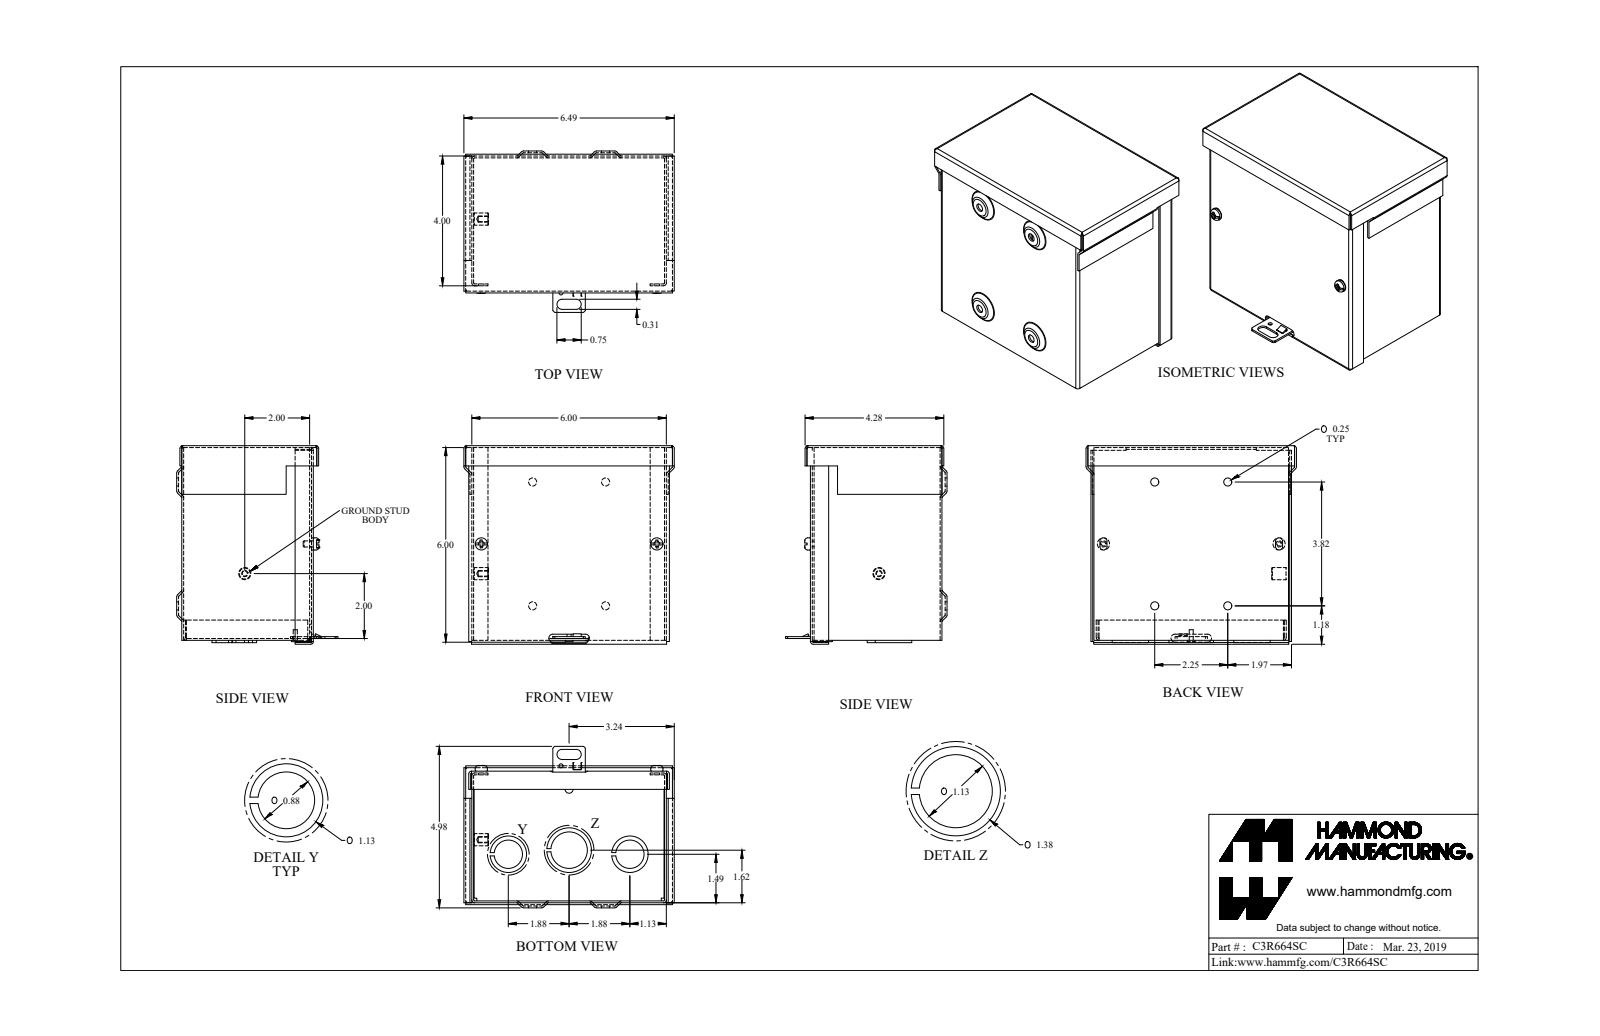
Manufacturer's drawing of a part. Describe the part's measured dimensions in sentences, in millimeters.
The part is named "C3R664SC_Default". Its 3-D file was written by "SolidWorks 2019 (CONFIG_CONTROL_DESIGN)". It is 9 solids with 353 faces: 182 planar, 97 cylindrical and 74 other. Overall it measures 164.8 by 155.4 by 126.4 millimeters. Its volume is 201 900 cubic millimeters and its surface area 282 600 square millimeters. Round holes: 4 of diameter 6.4, 2 of diameter 4.3, 2 of diameter 22.2, 1 of diameter 3.2, 1 of diameter 3.5, 1 of diameter 4, 1 of diameter 28.6. Round bosses or shafts: 3 of diameter 9.5, 2 of diameter 28.6, 2 of diameter 4.8, 1 of diameter 34.9, 1 of diameter 3.2. Partial cylindrical surfaces (rounded edges, fillets, slot ends): 21 of radius 0.7, 21 of radius 2.2, 8 of radius 3.2, 4 of radius 2.8, 2 of radius 4. The main face-to-face distances are 1.4, 101.6, 151, 152.4, 100.2, 1.4, 103, 149.5, 149.5, 151. The hole center spacings are 63, 108.7, 57.2, 97, 112.5, 19.4, 47.7, 47.8.
